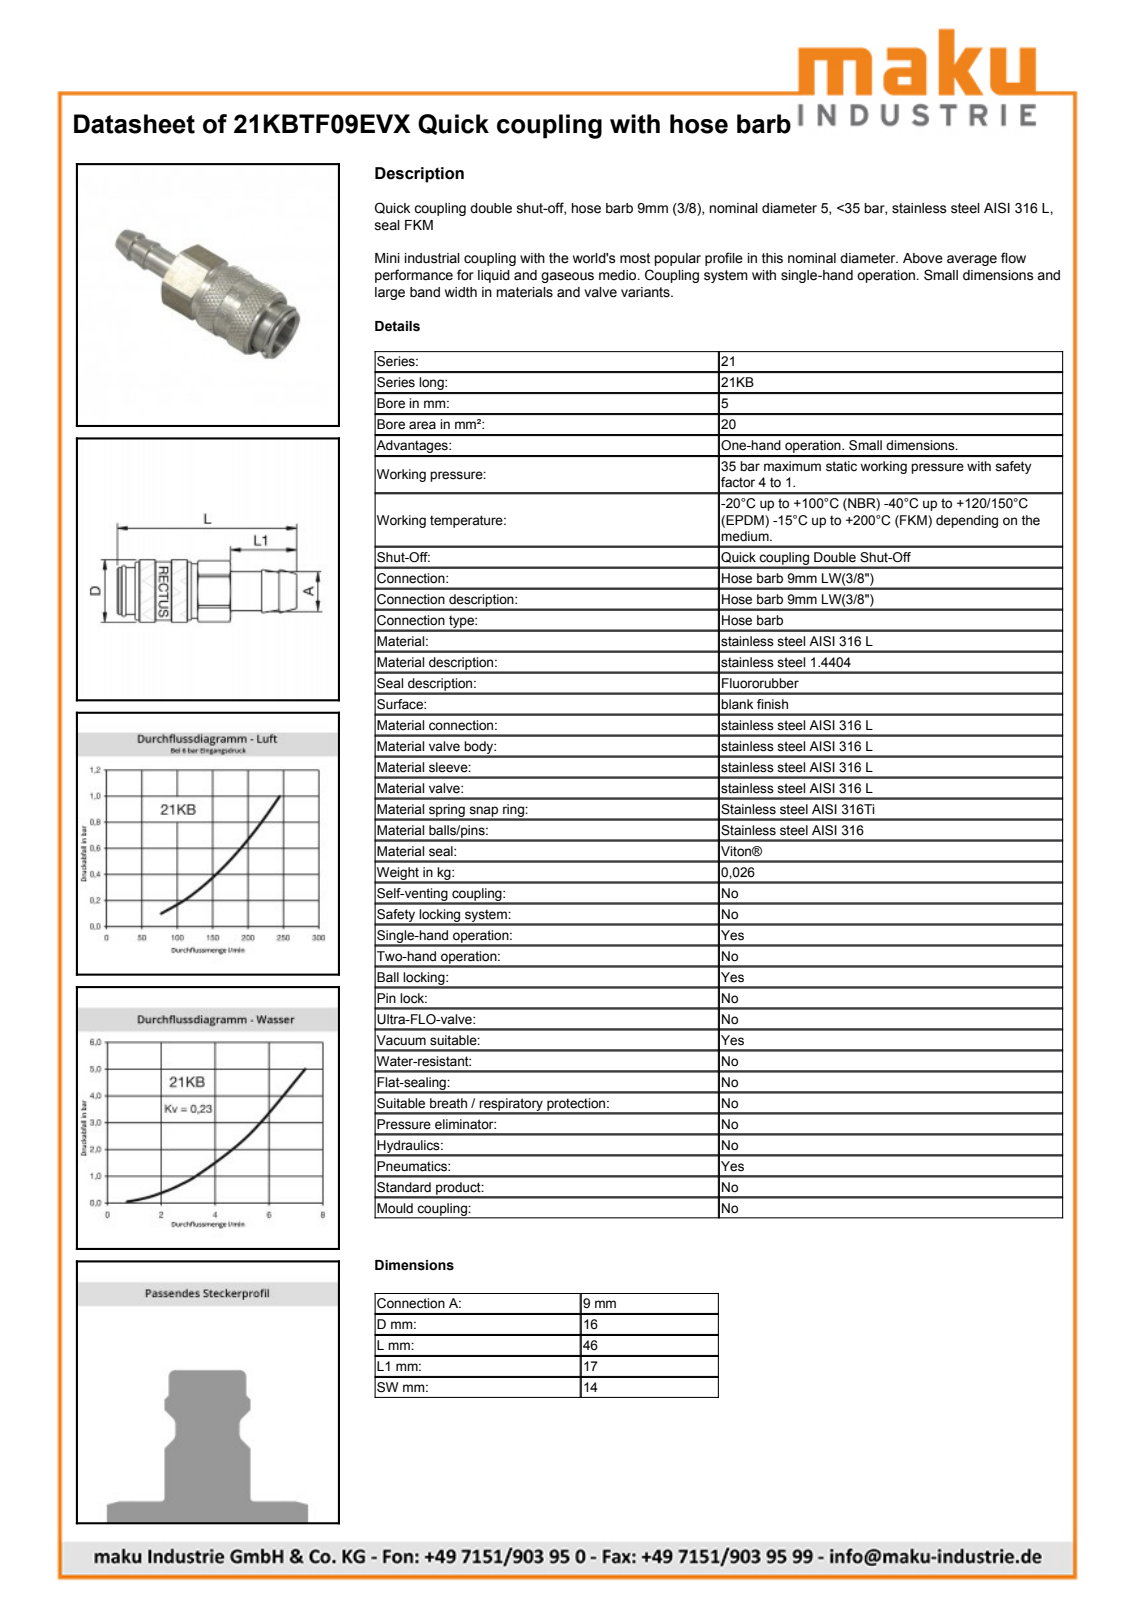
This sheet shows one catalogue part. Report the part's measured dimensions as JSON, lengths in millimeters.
{"part_name": "D111909", "step_written_by": "Autodesk Inventor 2013 (AUTOMOTIVE_DESIGN)", "units": "millimeters", "bodies": {"solids": 2, "faces": 473, "planar": 151, "cylindrical": 63, "other": 259}, "overall_size": [46.15, 16.15, 16.15], "volume_mm3": 5788, "surface_area_mm2": 3802, "round_holes": [[10.7, 1], [12.15, 1], [14, 1]], "round_bosses_or_shafts": [[16.15, 1], [15.1, 1], [12, 1], [11.81, 1], [11.15, 1], [9.52, 1], [9.05, 1]], "partial_cylinders_radius": [[7.45, 1], [7.9, 1]], "face_to_face_distances": [14, 29.15, 46.15, 17, 16.15, 13, 30, 4.56, 11.59, 24.59]}
